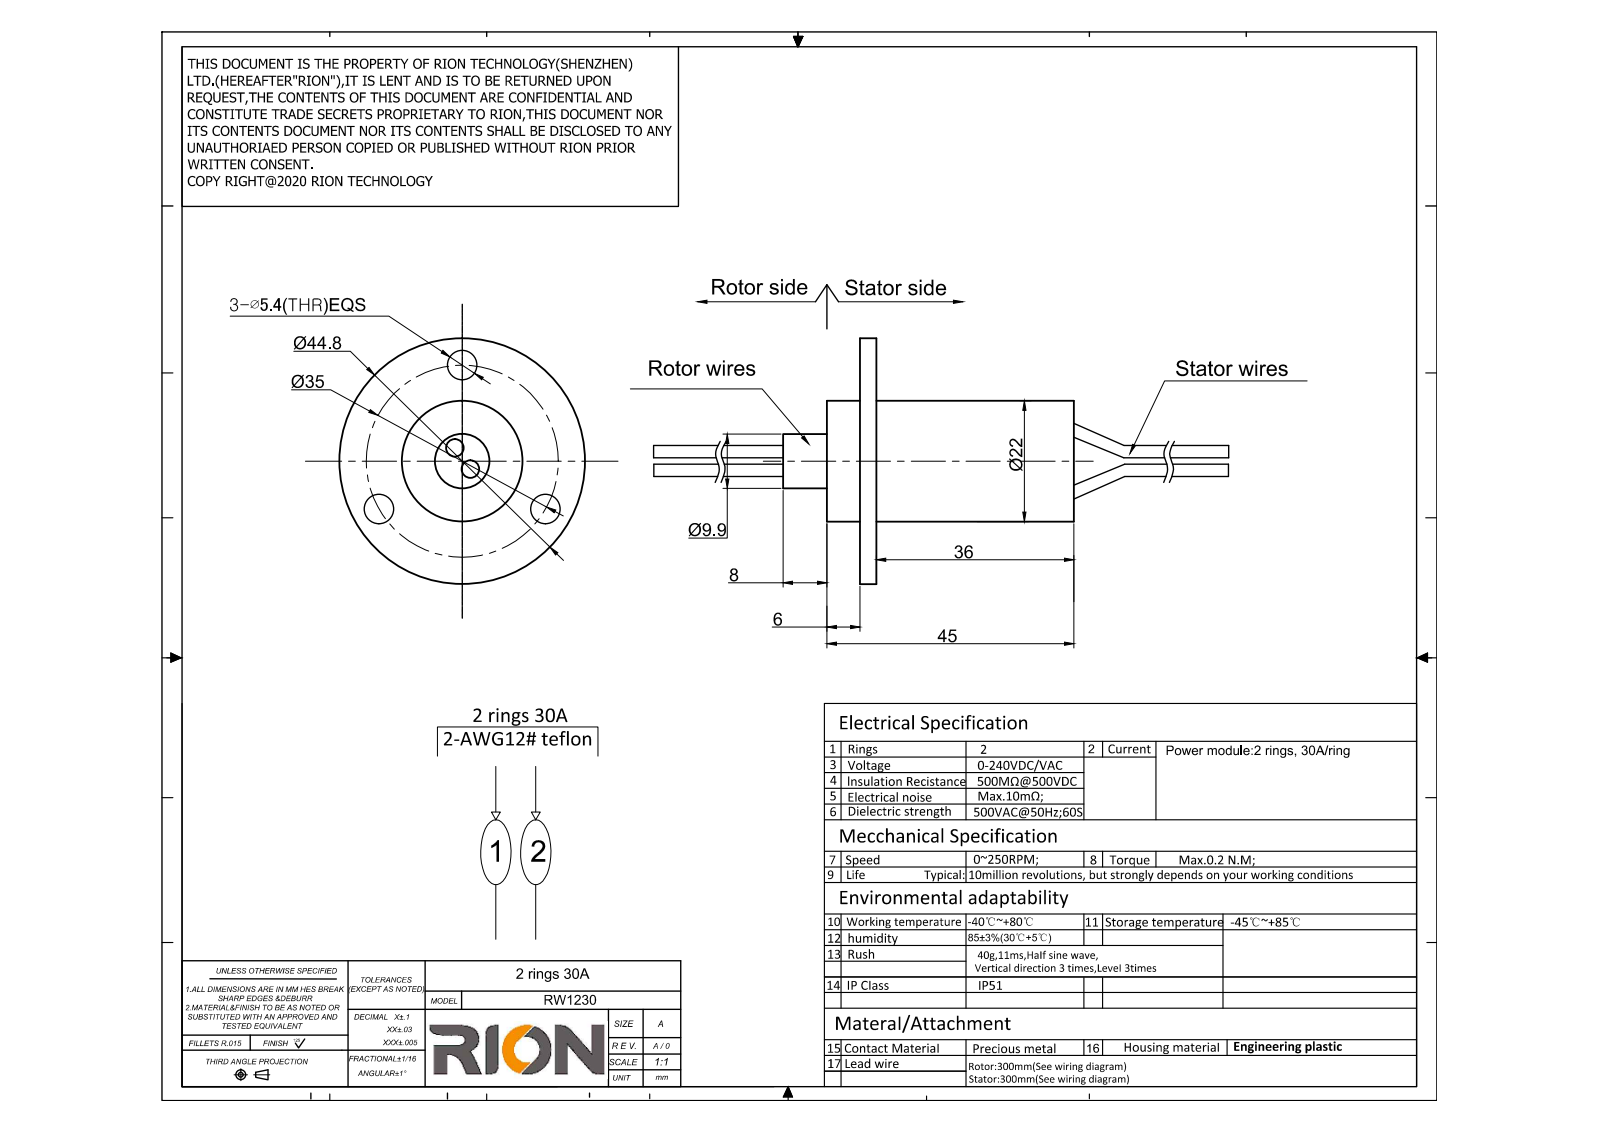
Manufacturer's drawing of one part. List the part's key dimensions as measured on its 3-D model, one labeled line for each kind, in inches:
Part name (STEP PRODUCT): RW1230
STEP written by: SolidWorks 2014 (CONFIG_CONTROL_DESIGN)
Units: inches
Bodies: 1 solid, 45 faces (13 planar, 30 cylindrical, 2 other)
Overall size (bounding box): 3.657 × 1.764 × 1.764
Volume: 1.278 in³ · Surface area: 11.95 in²
Round holes (diameter × count): ⌀0.213 ×3, ⌀0.295 ×1, ⌀0.398 ×1, ⌀0.787 ×1
Round bosses / shafts (diameter × count): ⌀0.126 ×4, ⌀1.764 ×1, ⌀0.866 ×1, ⌀0.783 ×1, ⌀0.39 ×1
Main face-to-face distances: 0.091, 1.535, 1.445, 0.236, 0.327, 1.772, 0.787, 2.87, 0.311, 0.547
Hole centre spacings: 0.689, 1.193, 1.194
